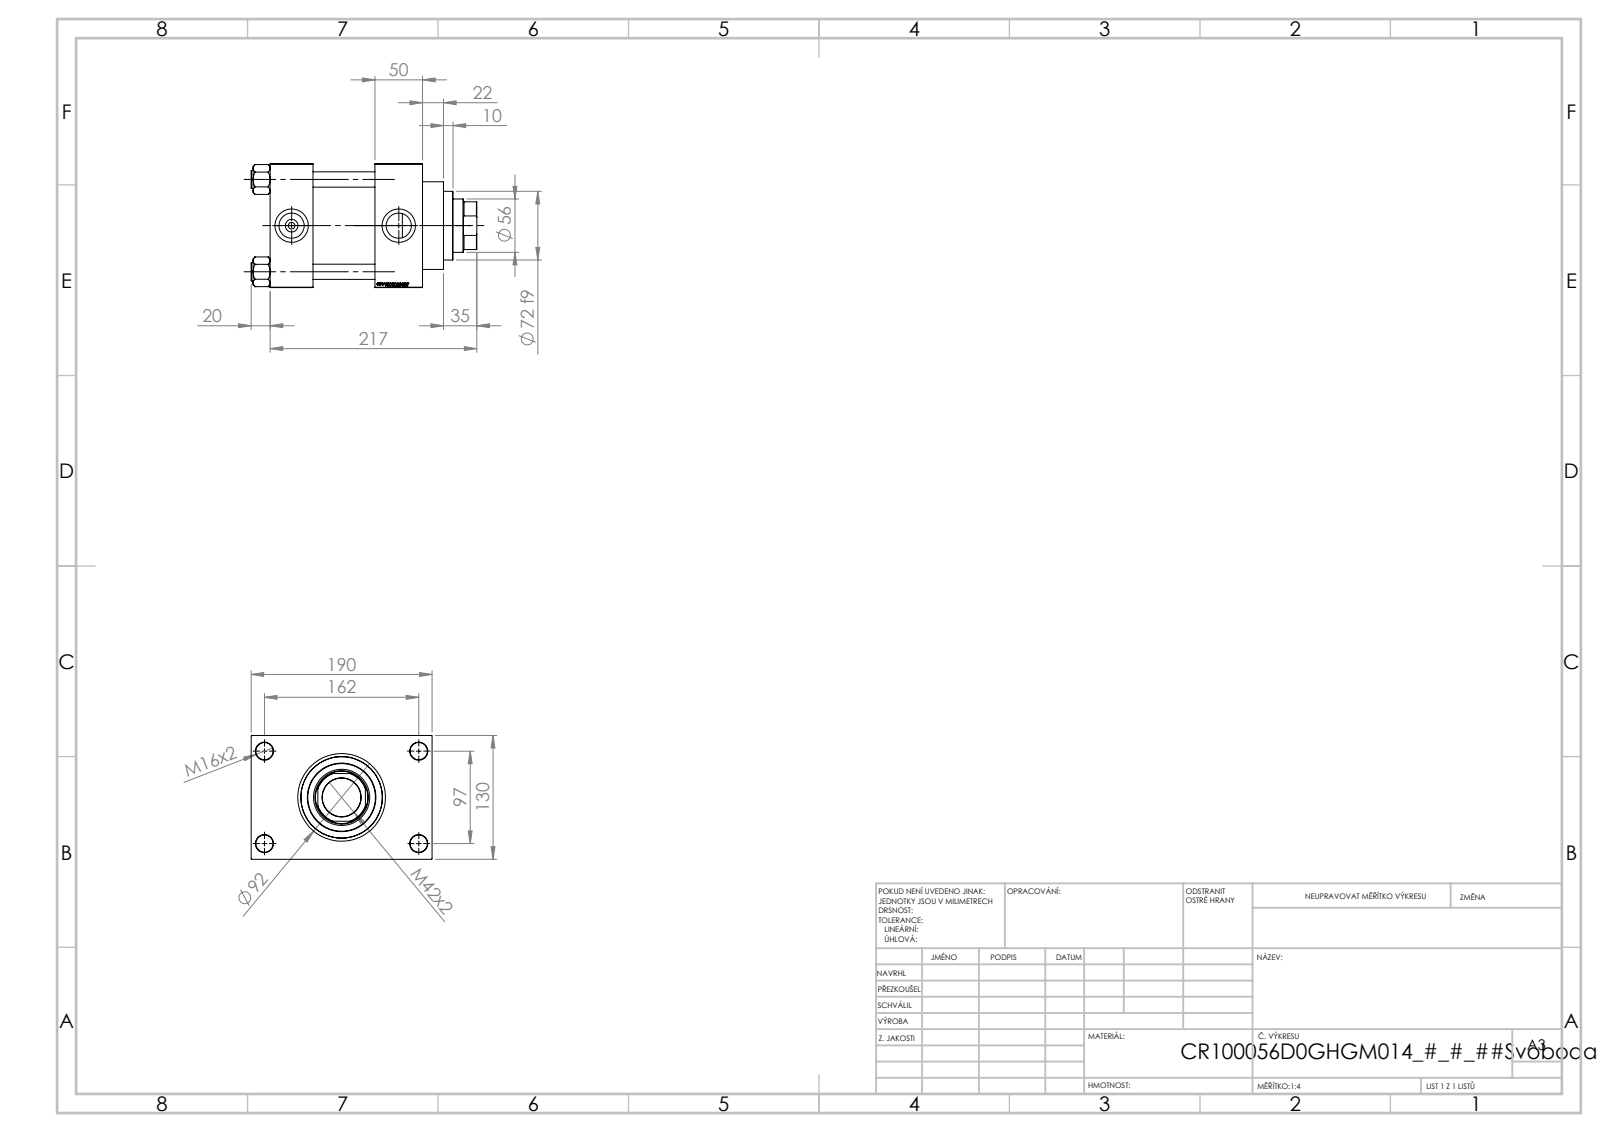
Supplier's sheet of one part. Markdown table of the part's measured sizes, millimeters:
| quantity | value |
| --- | --- |
| part name | V215CR_VCP_D; V215CR_D_TYCINKA; V215_VC_A; V215CR_D_Body (+1 more) |
| STEP written by | SolidWorks 2019 (CONFIG_CONTROL_DESIGN) |
| units | millimeters |
| bodies | 11 solids, 1151 faces (545 planar, 88 cylindrical, 518 other) |
| overall size | 237 × 190 × 130 |
| volume | 2 603 000 mm³ |
| surface area | 356 218 mm² |
| round holes (diameter × count) | 16 × 4, 18 × 4, 7 × 2, 26.44 × 2, 35 × 2, 40.5 × 1, 56 × 1, 59 × 1, 76 × 1, 85.5 × 1, 100 × 1 |
| round bosses / shafts (diameter × count) | 19 × 4, 106 × 1, 92 × 1, 72 × 1 |
| partial cylindrical surfaces (radius × count) | 27 × 1 |
| main face-to-face distances | 160, 130, 65, 50, 45, 110, 115, 30, 96, 14 |
| hole center spacings | 32.55, 68.52, 94.41, 96.9, 102.27, 129.45, 161.73, 97 |
